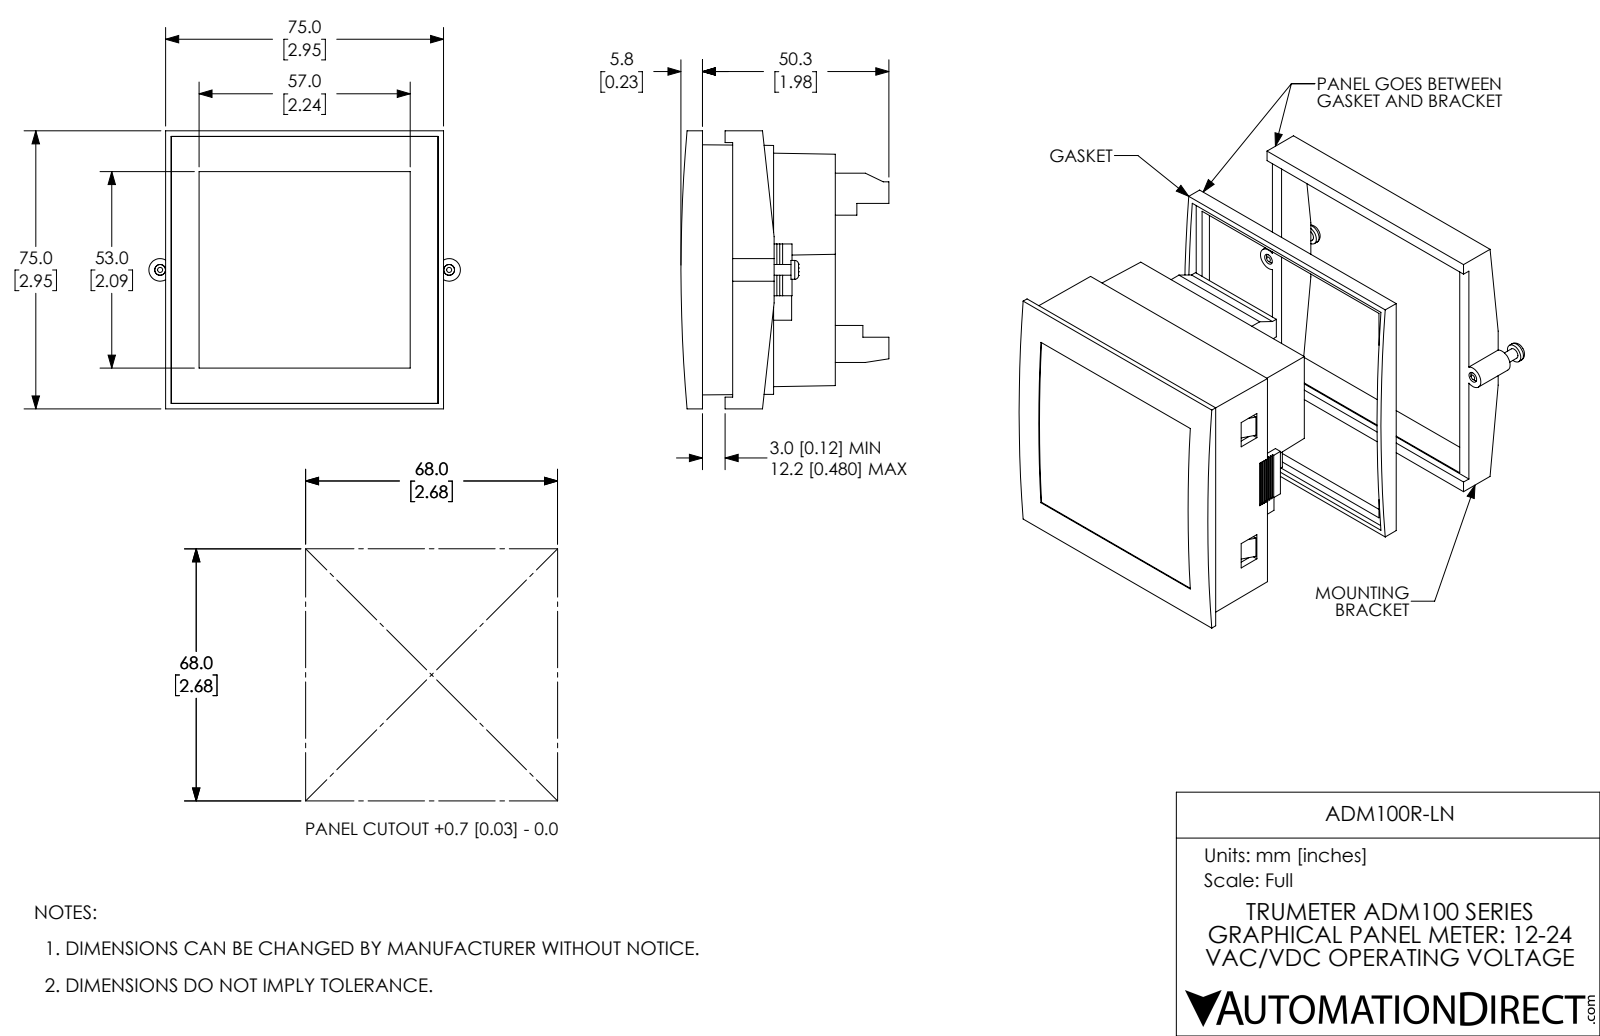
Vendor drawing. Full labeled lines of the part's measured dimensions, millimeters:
Part name (STEP PRODUCT): ADM100R-LN
STEP written by: SolidWorks 2021 (CONFIG_CONTROL_DESIGN)
Units: millimetres
Bodies: 23 solids, 419 faces (335 planar, 76 cylindrical, 8 other)
Overall size (bounding box): 84.1 × 75 × 56.1
Volume: 156 700 mm³ · Surface area: 58 480 mm²
Round holes (diameter × count): ⌀3.8 ×13, ⌀2.9 ×2
Round bosses / shafts (diameter × count): ⌀3.8 ×13, ⌀5.1 ×2, ⌀2.9 ×2
Partial cylindrical surfaces — rounded edges, fillets, slot ends (radius × count): R3 ×2, R432.7 ×2
Main face-to-face distances: 1.9, 7.7, 6, 69, 67.5, 2.3, 3.8, 71.2, 65.6, 29
Hole centre spacings: 42, 5.1, 42.6, 10.2, 43.8, 15.2, 45.5, 20.3
